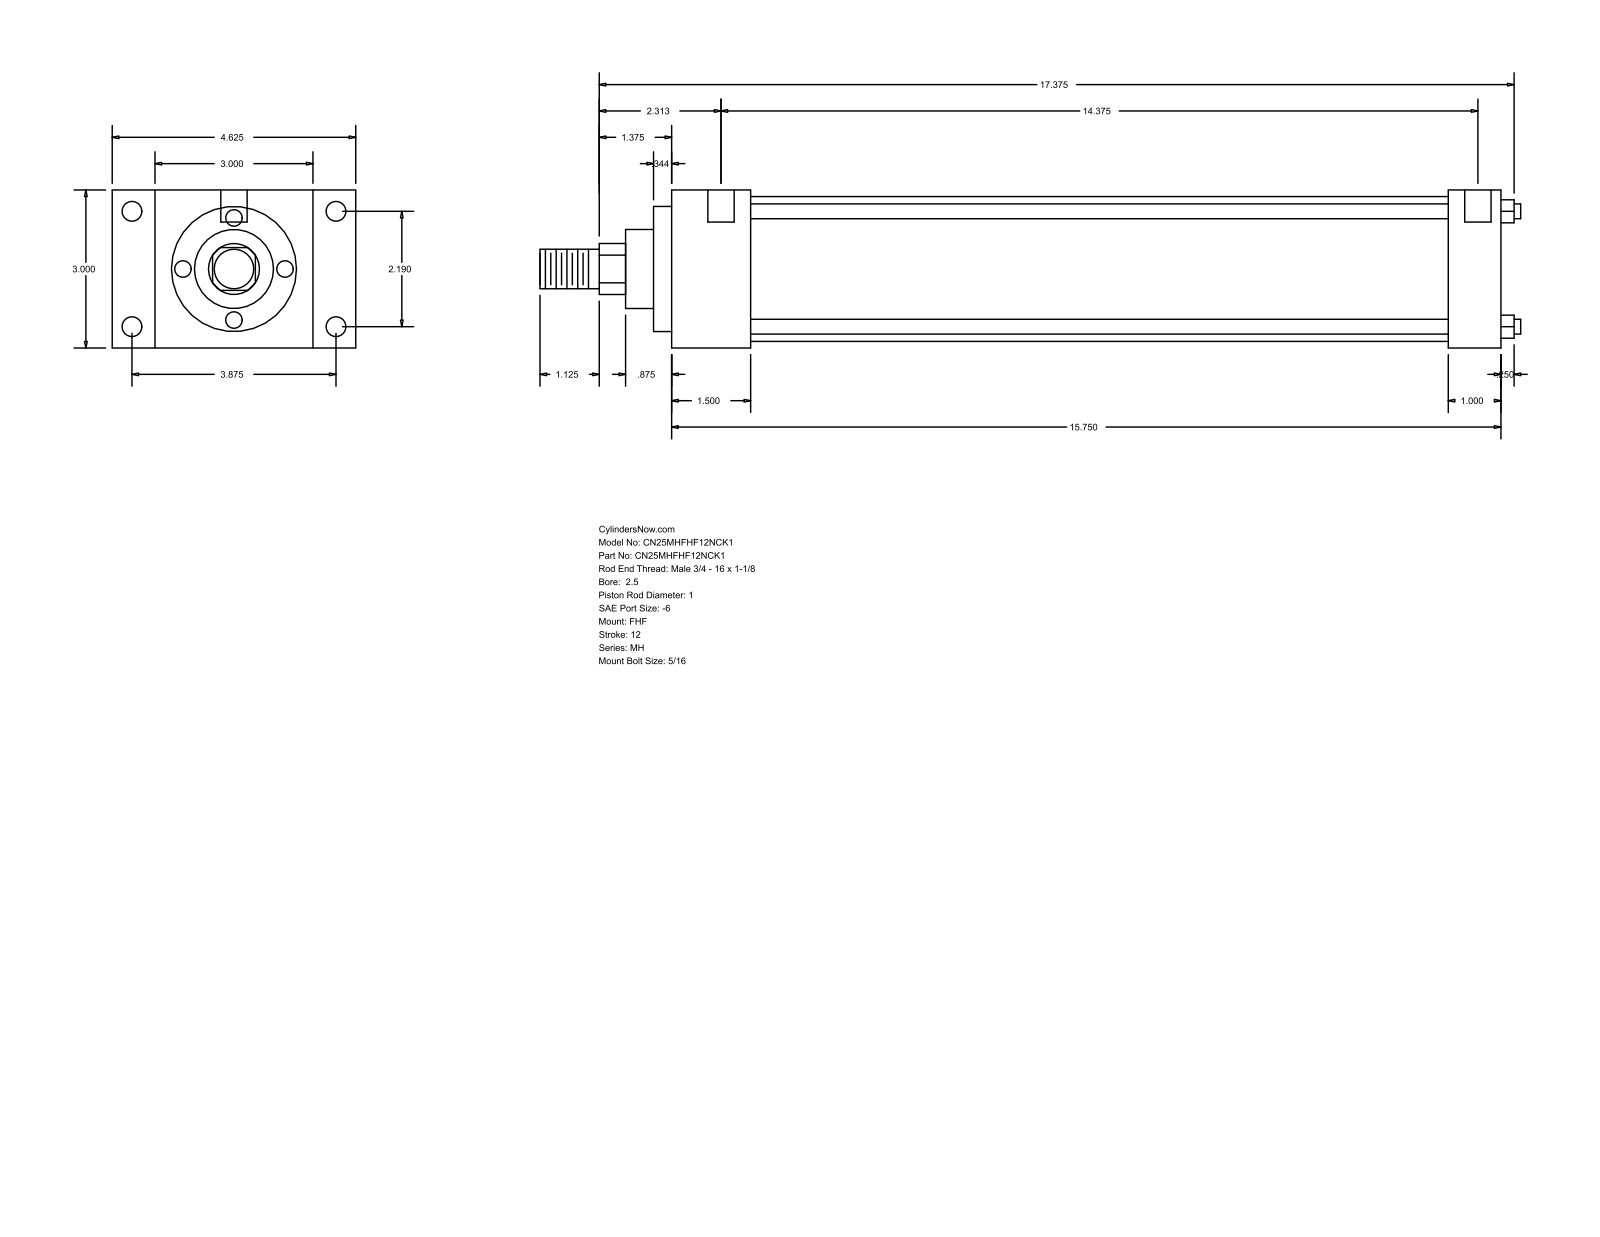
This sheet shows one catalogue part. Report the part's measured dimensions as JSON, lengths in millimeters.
{"part_name": "MH_FHF__0250_1", "step_written_by": "GSSL Pune (CONFIG_CONTROL_DESIGN)", "units": "millimeters", "bodies": {"solids": 0, "faces": 90, "planar": 61, "cylindrical": 29, "other": 0}, "overall_size": [473.07, 117.47, 76.2], "round_holes": [[5.56, 4], [9.53, 4], [12.7, 2]], "round_bosses_or_shafts": [[7.14, 4], [69.85, 1], [60.33, 1], [38.1, 1], [25.4, 1], [19.05, 1]], "partial_cylinders_radius": [[12.29, 1]], "face_to_face_distances": [76.2, 400.06, 38.11, 361.95, 20.64, 96.84, 117.48, 374.65, 336.54, 25.41], "hole_center_spacings": [55.62, 98.42, 113.05, 373.06, 3.18, 4.76, 365.12, 368.3]}
